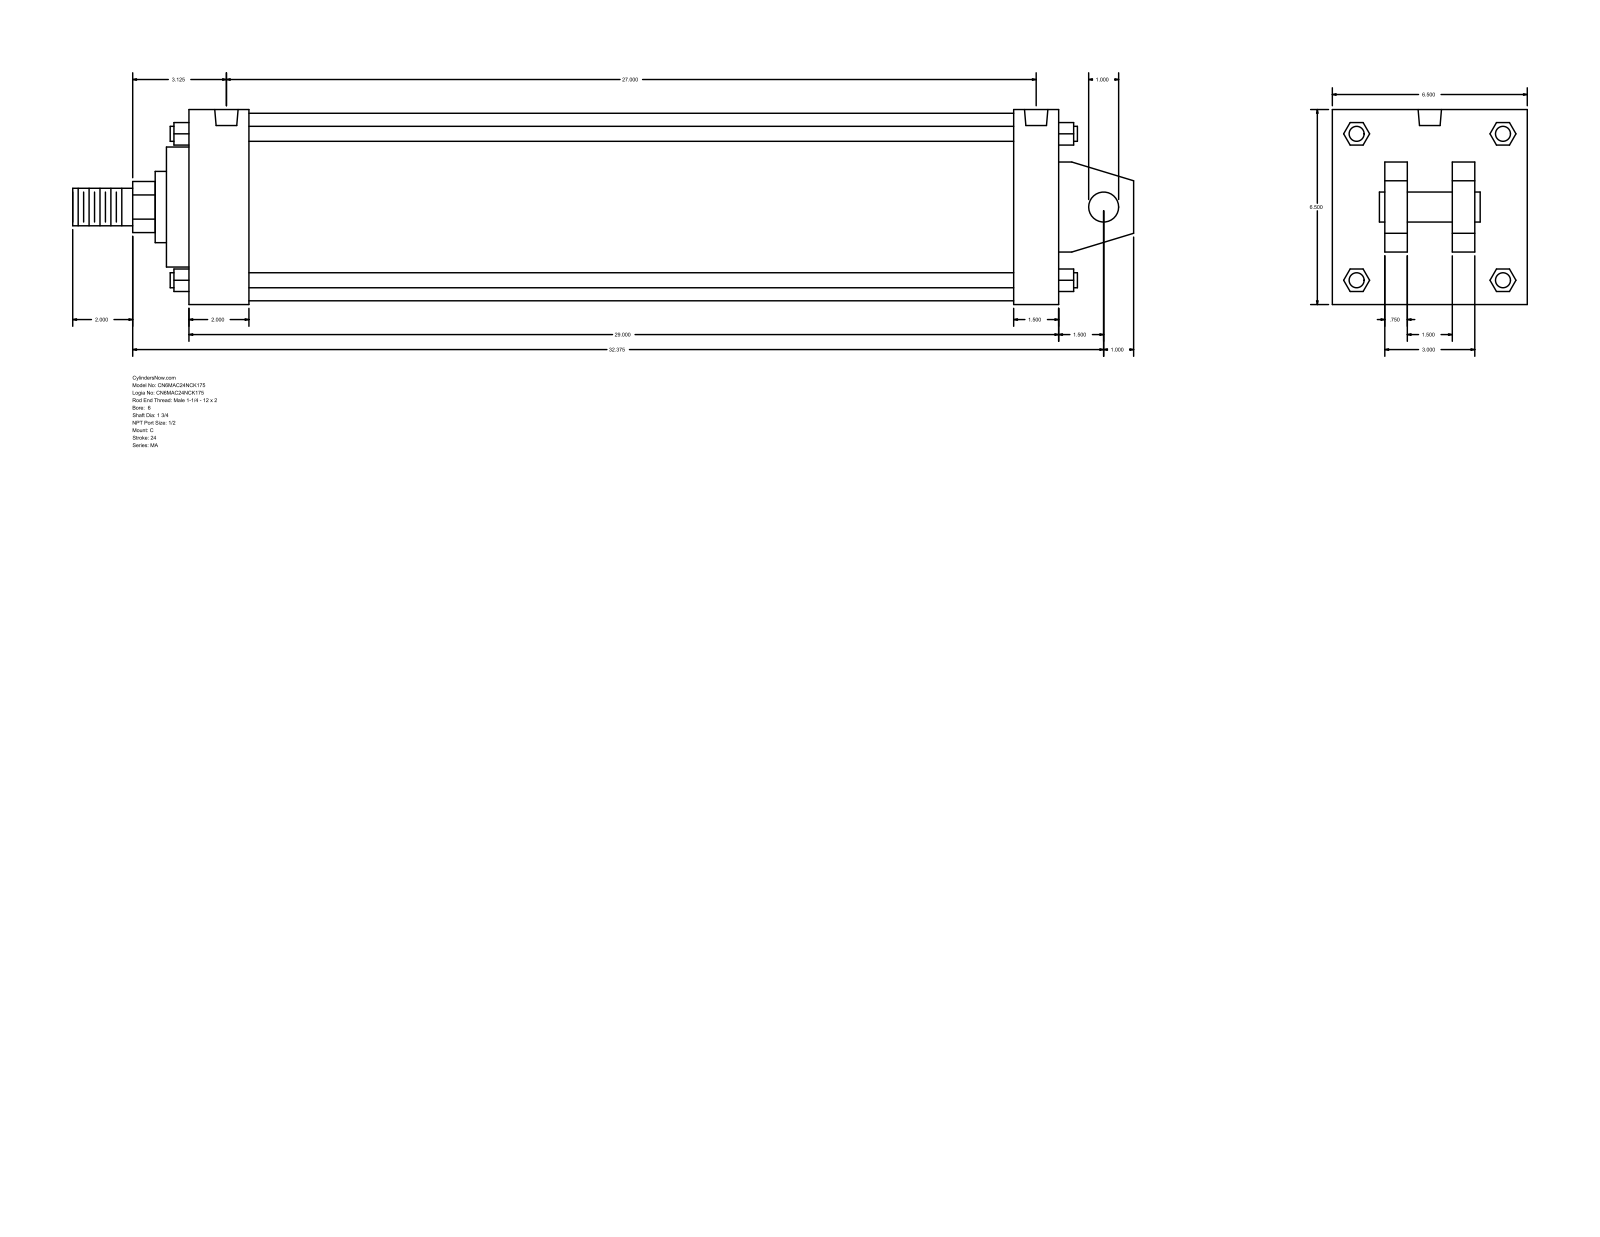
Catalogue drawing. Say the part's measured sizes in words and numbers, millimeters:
The part is named "MA_C__0600_1.75". Its 3-D file was written by "GSSL Pune (CONFIG_CONTROL_DESIGN)". It is 0 solids with 141 faces: 109 planar, 32 cylindrical and 0 other. Overall it measures 898.52 by 165.1 by 165.1 millimeters. Round holes: 4 of diameter 17.46, 2 of diameter 19.77. Round bosses or shafts: 4 of diameter 12.7, 1 of diameter 158.75, 1 of diameter 101.6, 1 of diameter 60.33, 1 of diameter 44.45, 1 of diameter 31.75, 1 of diameter 25.4. Partial cylindrical surfaces (rounded edges, fillets, slot ends): 1 of radius 21.63. The main face-to-face distances are 165.1, 736.61, 19.05, 63.5, 101.6, 50.8, 44.45, 120.65, 698.5, 57.15. The hole center spacings are 685.79.
